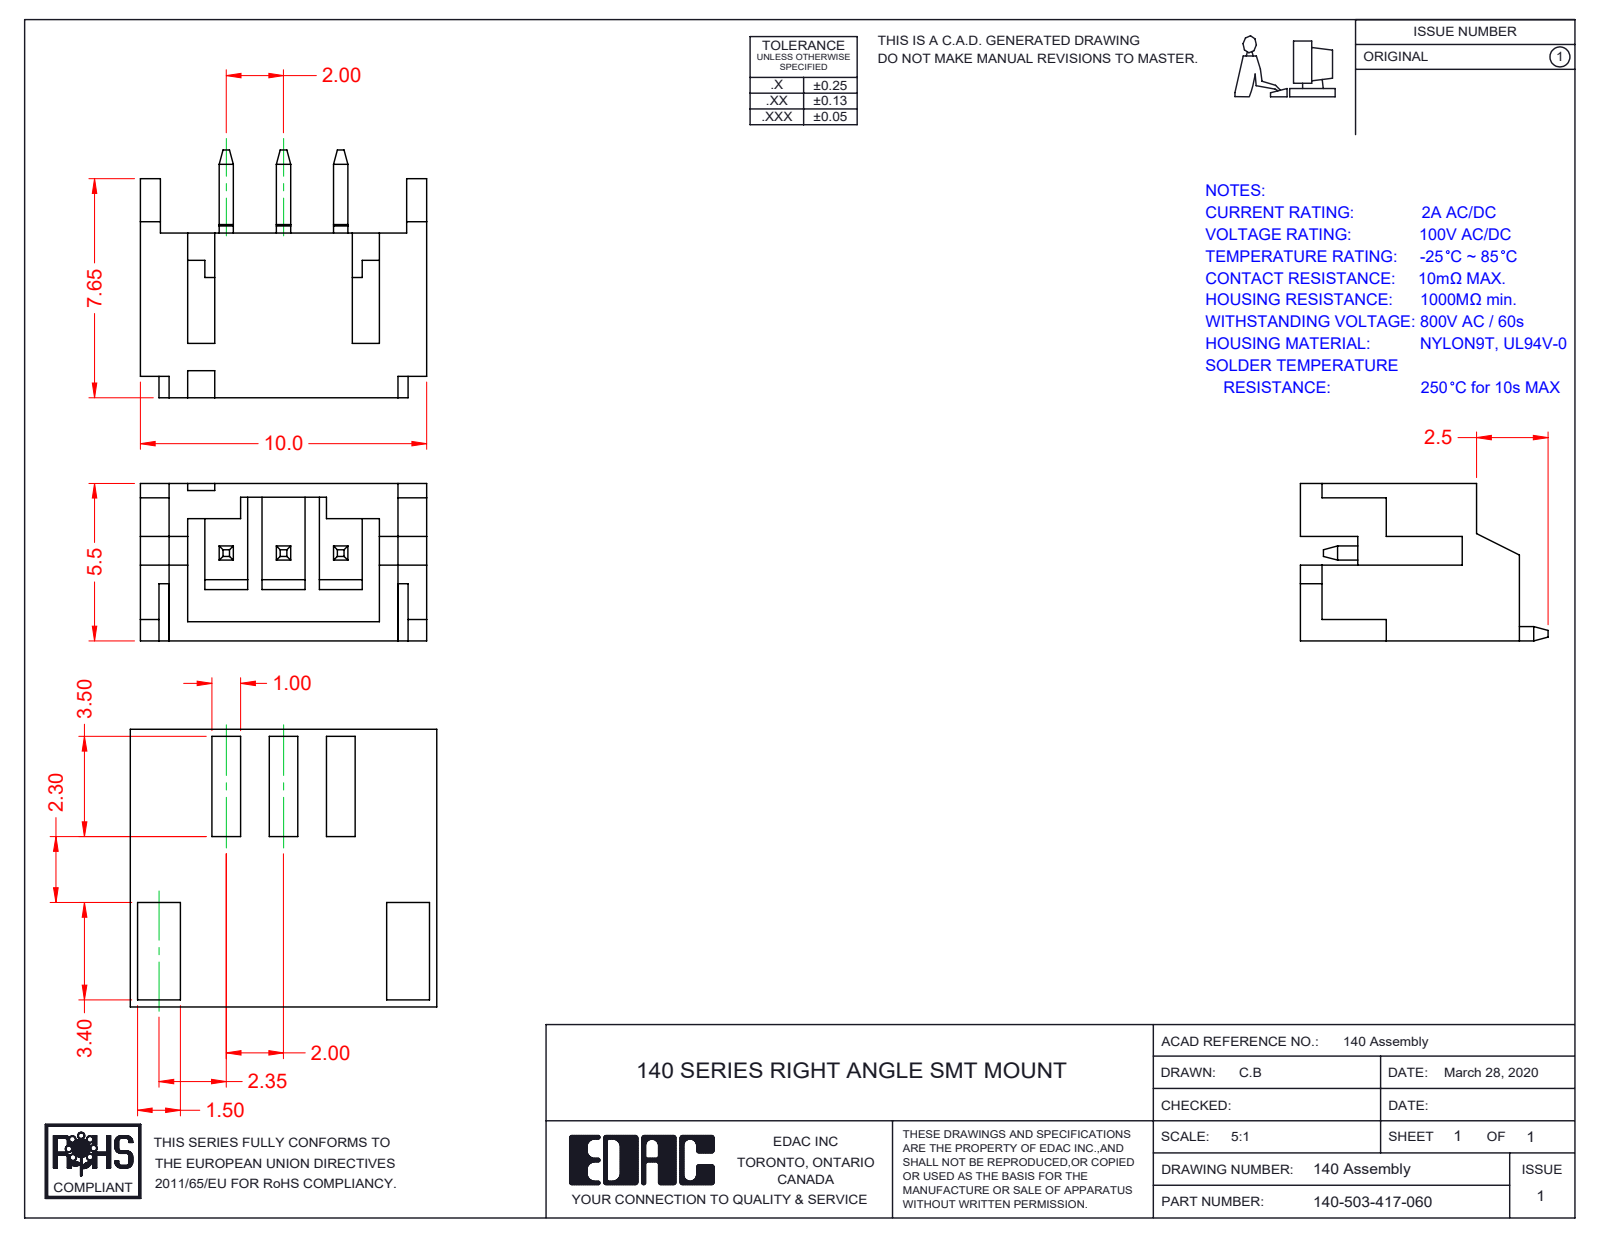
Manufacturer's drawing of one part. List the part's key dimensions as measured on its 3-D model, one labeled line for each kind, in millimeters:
Part name (STEP PRODUCT): RA SMT Pad; RA SMT Housing_503; RA SMT Contact; 140-503-417-060
STEP written by: SolidWorks 2016 (CONFIG_CONTROL_DESIGN)
Units: millimetres
Bodies: 6 solids, 218 faces (206 planar, 12 cylindrical, 0 other)
Overall size (bounding box): 10 × 8.65 × 5.5
Volume: 166 mm³ · Surface area: 582 mm²
Partial cylindrical surfaces — rounded edges, fillets, slot ends (radius × count): R0.55 ×2
Main face-to-face distances: 0.65, 1, 5.5, 8.35, 1.65, 0.95, 9, 0.5, 7.35, 0.67
